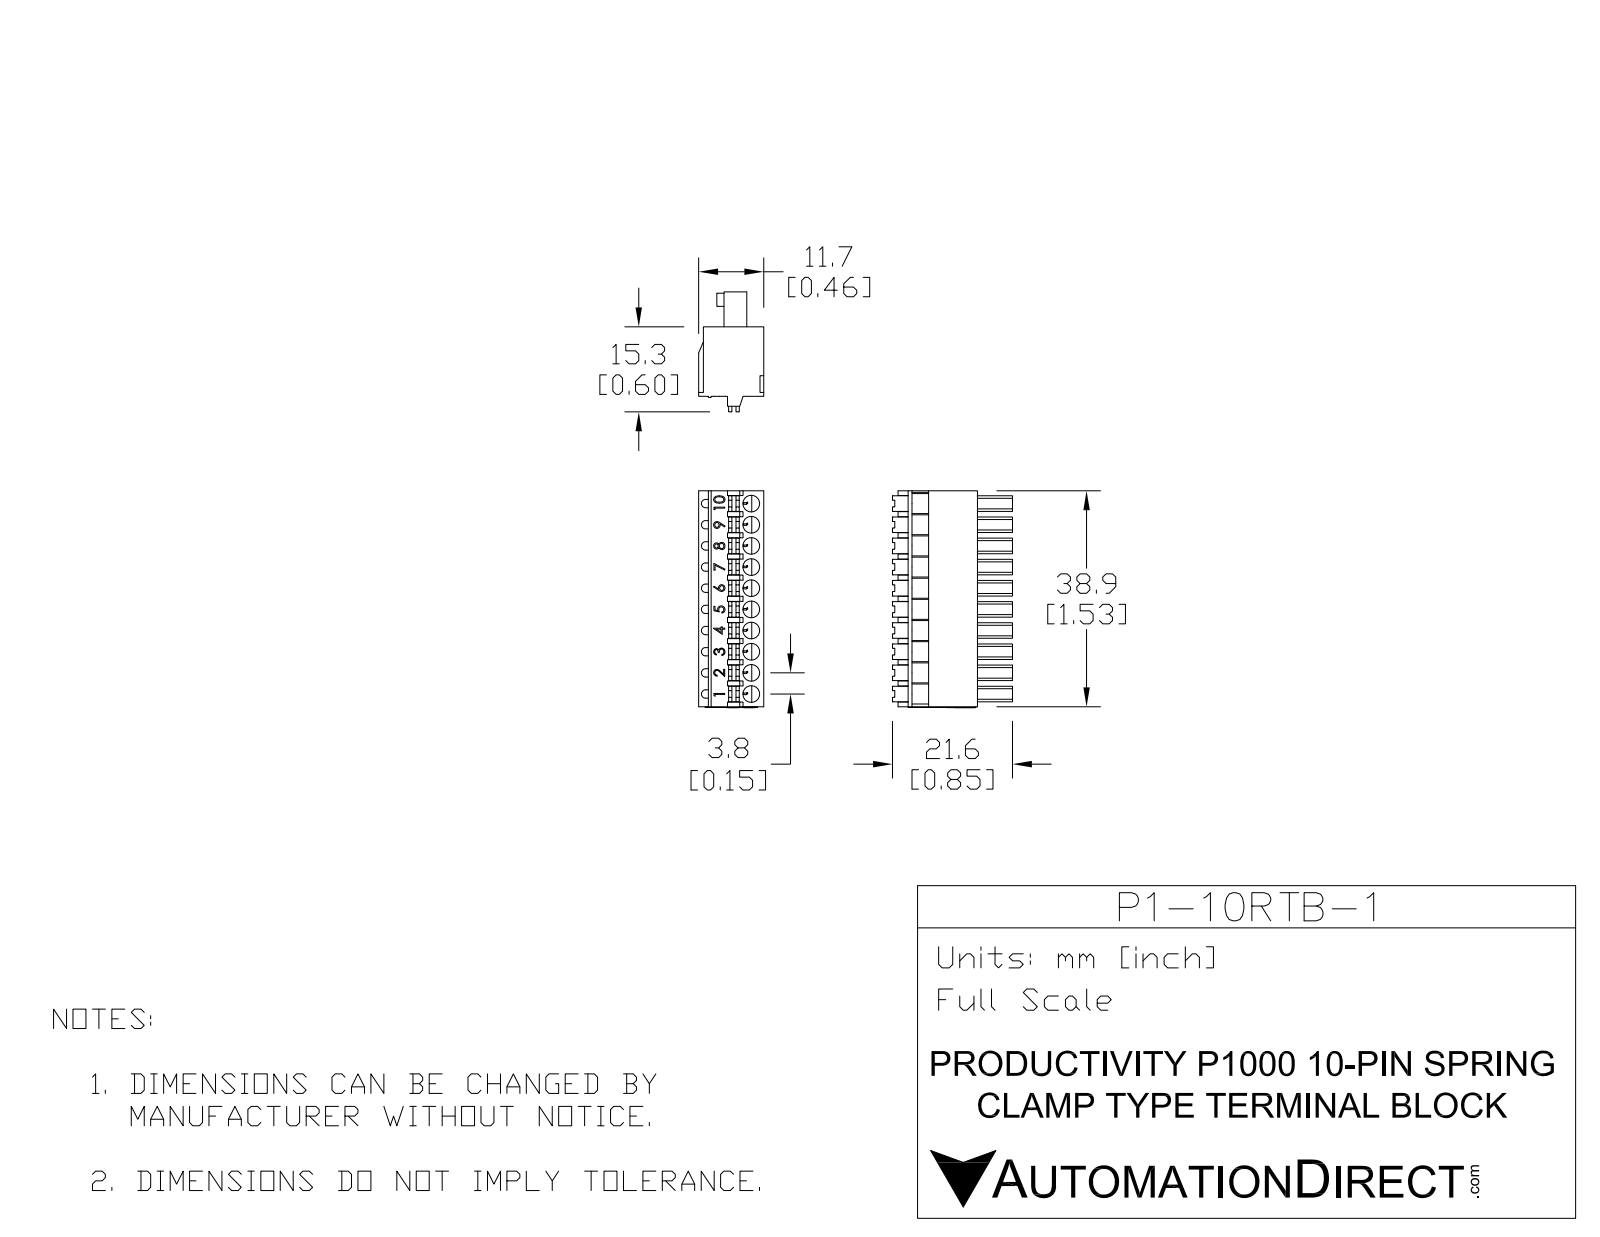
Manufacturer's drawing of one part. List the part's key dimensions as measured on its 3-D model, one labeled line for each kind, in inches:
Part name (STEP PRODUCT): P1-10RTB-1
STEP written by: SolidWorks 2016 (AUTOMOTIVE_DESIGN)
Units: inches
Bodies: 2 solids, 1204 faces (876 planar, 215 cylindrical, 113 other)
Overall size (bounding box): 1.537 × 0.85 × 0.462
Volume: 0.345 in³ · Surface area: 8.632 in²
Round holes (diameter × count): ⌀0.063 ×10, ⌀0.118 ×10
Partial cylindrical surfaces — rounded edges, fillets, slot ends (radius × count): R0.03 ×30, R0.008 ×20, R0.08 ×11, R0.049 ×10, R0.065 ×10, R0.004 ×4, R0.012 ×4
Main face-to-face distances: 0.15, 0.3, 0.45, 0.492, 0.035, 0.428, 0.11, 0.6, 0.75, 0.9
Hole centre spacings: 0.15, 0.187, 0.3, 0.32, 0.45, 0.464, 0.6, 0.611
